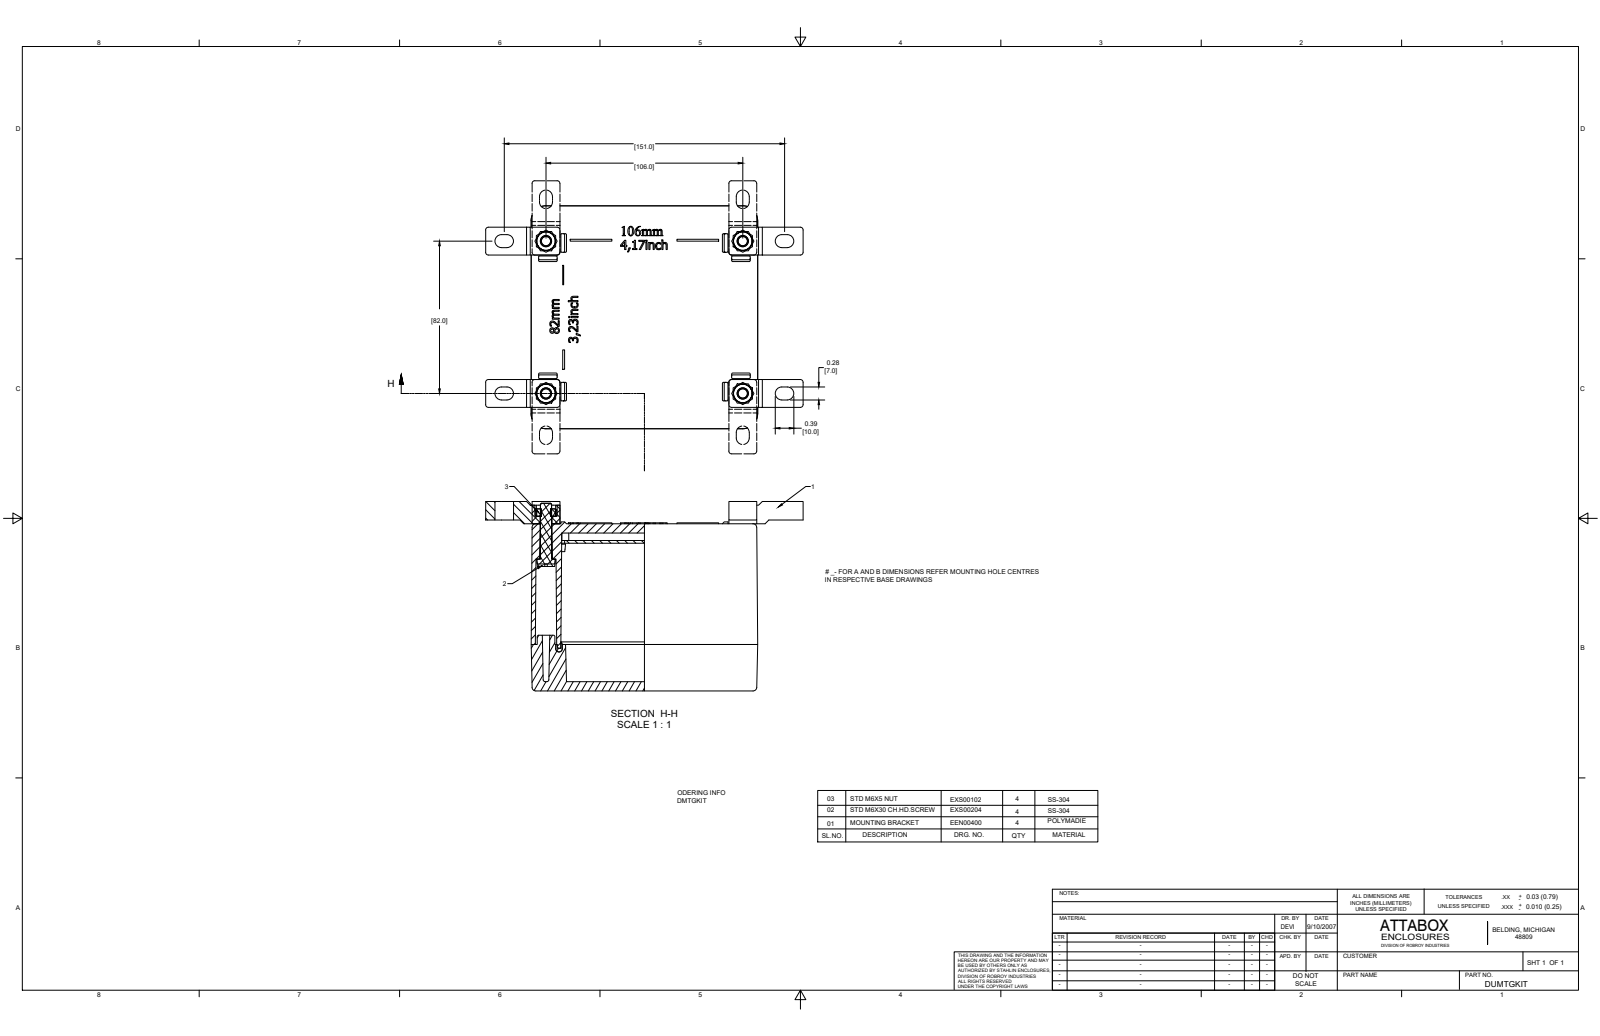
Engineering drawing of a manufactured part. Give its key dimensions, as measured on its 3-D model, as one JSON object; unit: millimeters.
{"part_name": "DUMTGKIT", "step_written_by": "SolidWorks 2018 (AUTOMOTIVE_DESIGN)", "units": "millimeters", "bodies": {"solids": 3, "faces": 57, "planar": 34, "cylindrical": 9, "other": 14}, "overall_size": [40, 35, 15], "volume_mm3": 6190, "surface_area_mm2": 3881, "round_holes": [[4.9, 1], [6.2, 1]], "round_bosses_or_shafts": [[6, 1]], "partial_cylinders_radius": [[1.5, 4], [3.5, 2]], "face_to_face_distances": [2, 10, 15, 4, 8, 12, 6, 40, 23, 27]}
